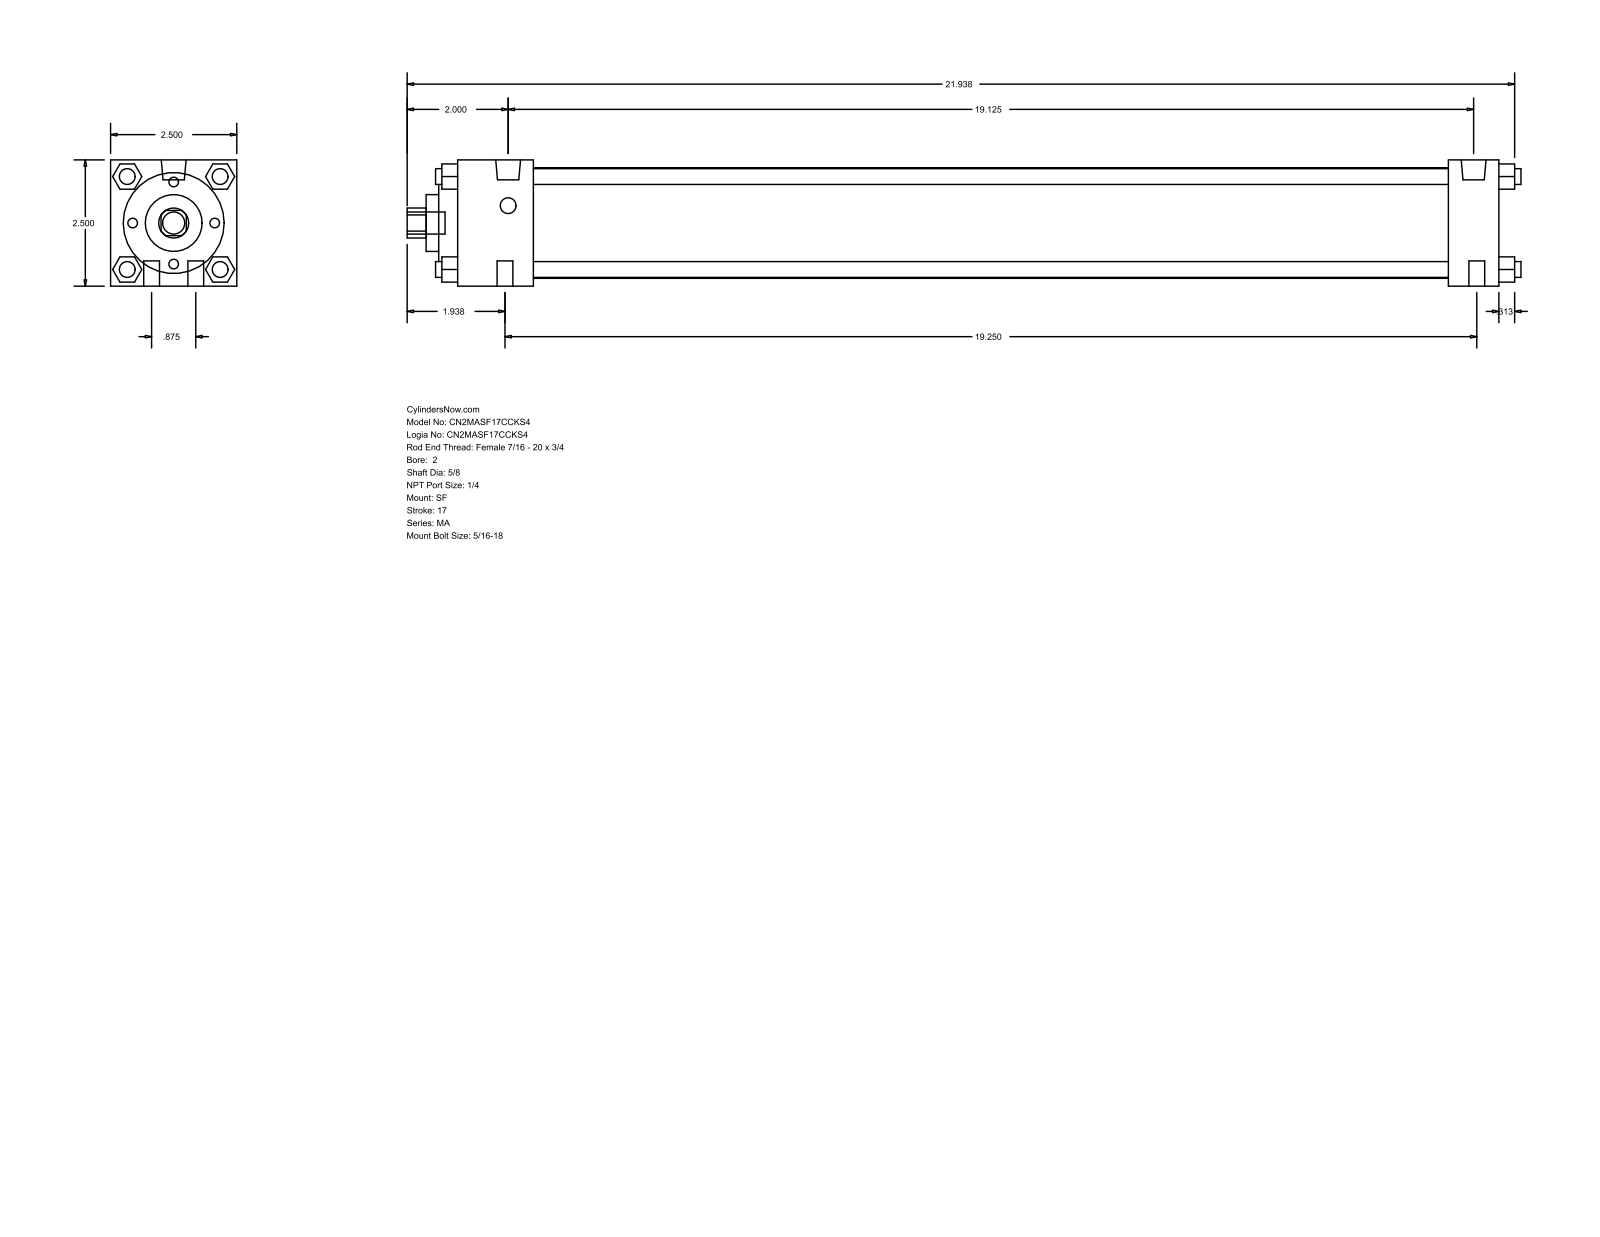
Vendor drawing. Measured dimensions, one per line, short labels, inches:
name: MA_SF__0200_0.625
written by: GSSL Pune (CONFIG_CONTROL_DESIGN)
unit: in
bodies: 0 solids, 126 faces (95 planar, 31 cylindrical, 0 other)
size: 22.063 × 2.5 × 2.5
holes: 1× ⌀0.625, 1× ⌀1.125, 1× ⌀2, 1× ⌀2.19
bosses: 10× ⌀0.313, 2× ⌀0.492, 1× ⌀0.437
rounds: 1× R0.297
face distances: 2.5, 0.5, 1.5, 0.375, 20.625, 19.625, 1, 18.125, 19.125, 1.875
